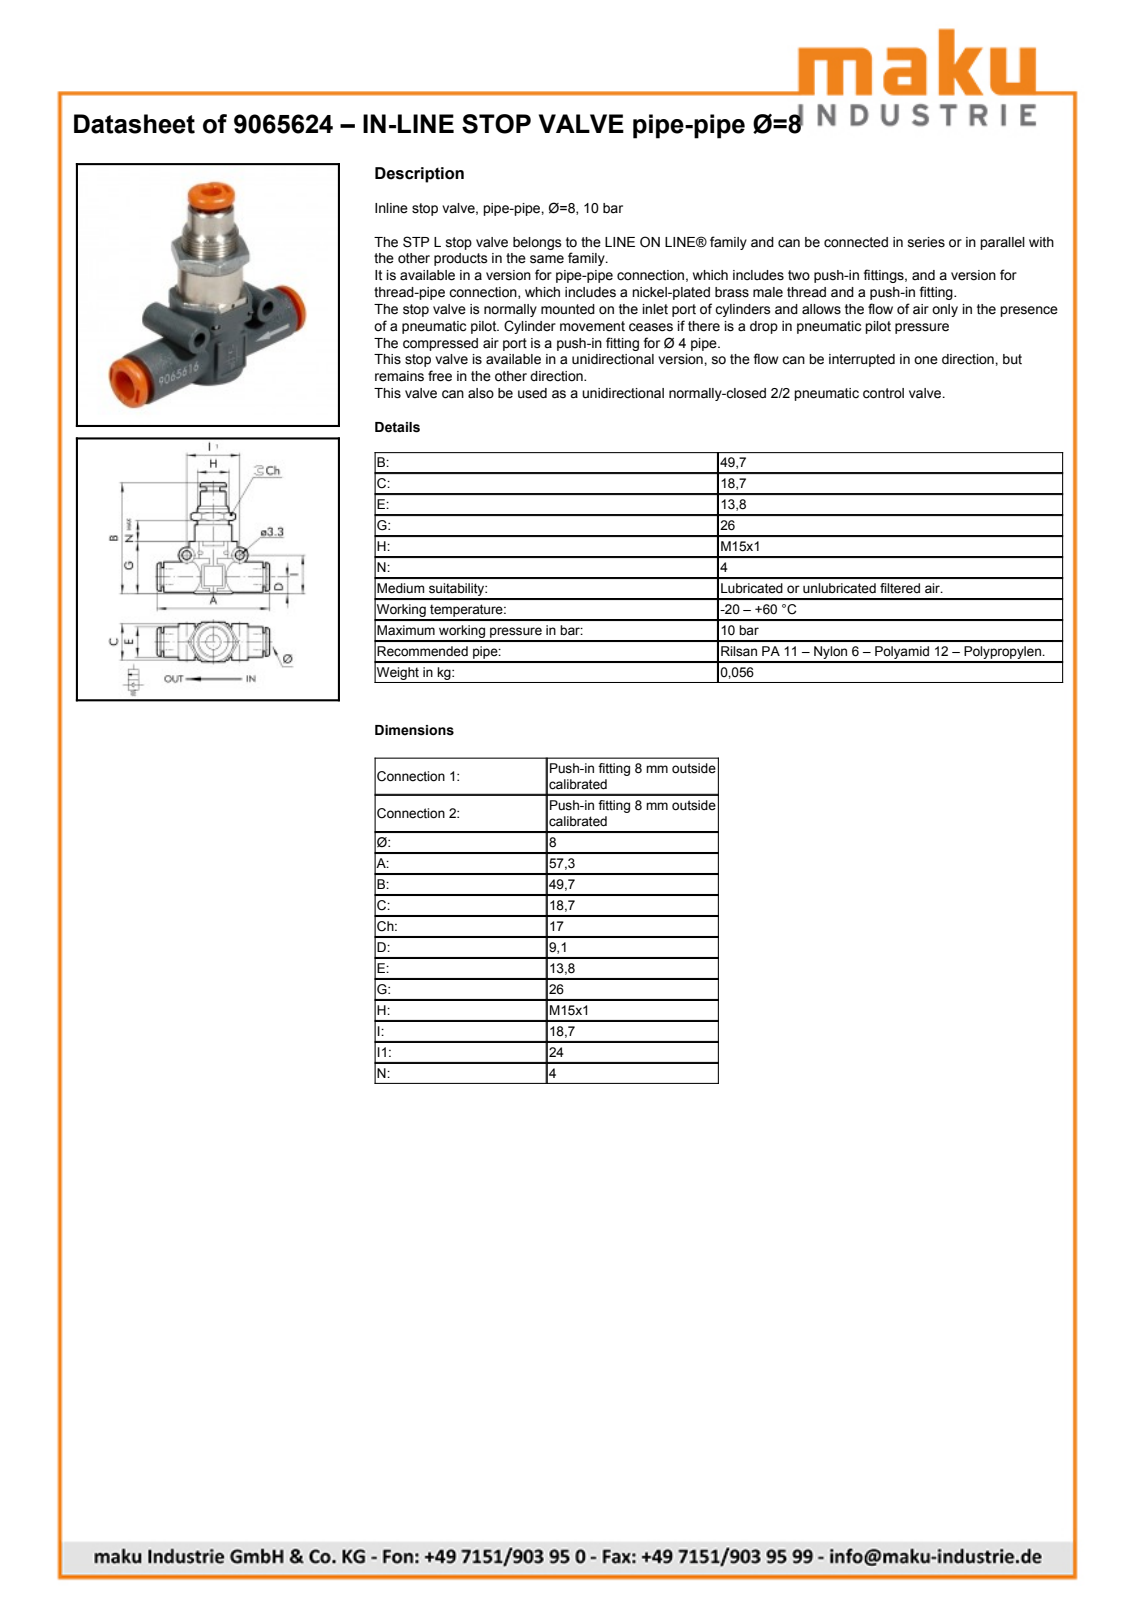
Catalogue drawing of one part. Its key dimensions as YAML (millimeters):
part_name: "9065624; LINE-ON-LINE D8 PNV_L-body; LINE-ON-LINE D8 VNR-L bushing; LINE ON LINE D8 plate (+1 more)"
step_written_by: "PARTsolutions (AUTOMOTIVE_DESIGN)"
units: millimeters
bodies: {solids: 5, faces: 185, planar: 120, cylindrical: 53, other: 12}
overall_size: [57.3, 49.7, 18.7]
volume: 11467
surface_area: 10734
round_holes:
  - {diameter: 3.3, count: 2}
  - {diameter: 6, count: 2}
  - {diameter: 5.53, count: 1}
  - {diameter: 6.2, count: 1}
  - {diameter: 8.1, count: 1}
  - {diameter: 11, count: 1}
  - {diameter: 11.65, count: 1}
  - {diameter: 12.5, count: 1}
  - {diameter: 15, count: 1}
round_bosses_or_shafts:
  - {diameter: 6, count: 2}
  - {diameter: 18.8, count: 1}
  - {diameter: 18, count: 1}
  - {diameter: 13.8, count: 1}
  - {diameter: 13.6, count: 1}
  - {diameter: 12.8, count: 1}
  - {diameter: 11, count: 1}
  - {diameter: 10.3, count: 1}
partial_cylinders:
  - {radius: 3.75, count: 1}
  - {radius: 10.35, count: 1}
  - {radius: 11.45, count: 1}
face_to_face_distances: [24.1, 4.1, 20, 1.9, 1.7, 18.5, 15.55, 37.95, 23, 20.5]
hole_center_spacings: [15.37, 24]
